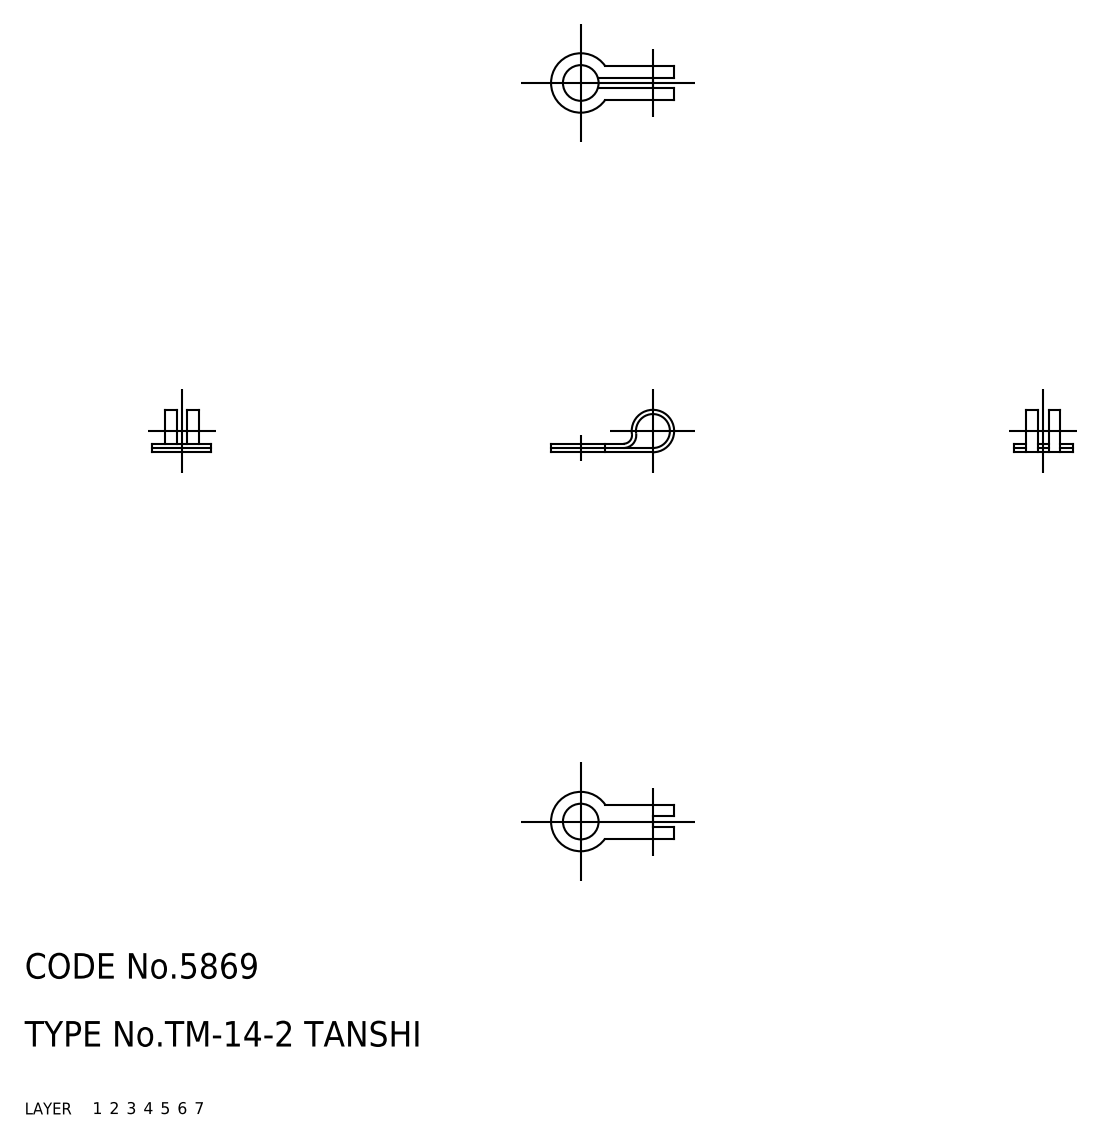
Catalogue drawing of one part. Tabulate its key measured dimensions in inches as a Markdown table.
| quantity | value |
| --- | --- |
| part name | terminal |
| STEP written by | CADfix (AUTOMOTIVE_DESIGN) |
| units | inches |
| bodies | 1 solid, 22 faces (0 planar, 0 cylindrical, 22 other) |
| overall size | 0.571 × 0.276 × 0.197 |
| volume | 0.003 in³ |
| surface area | 0.446 in² |
